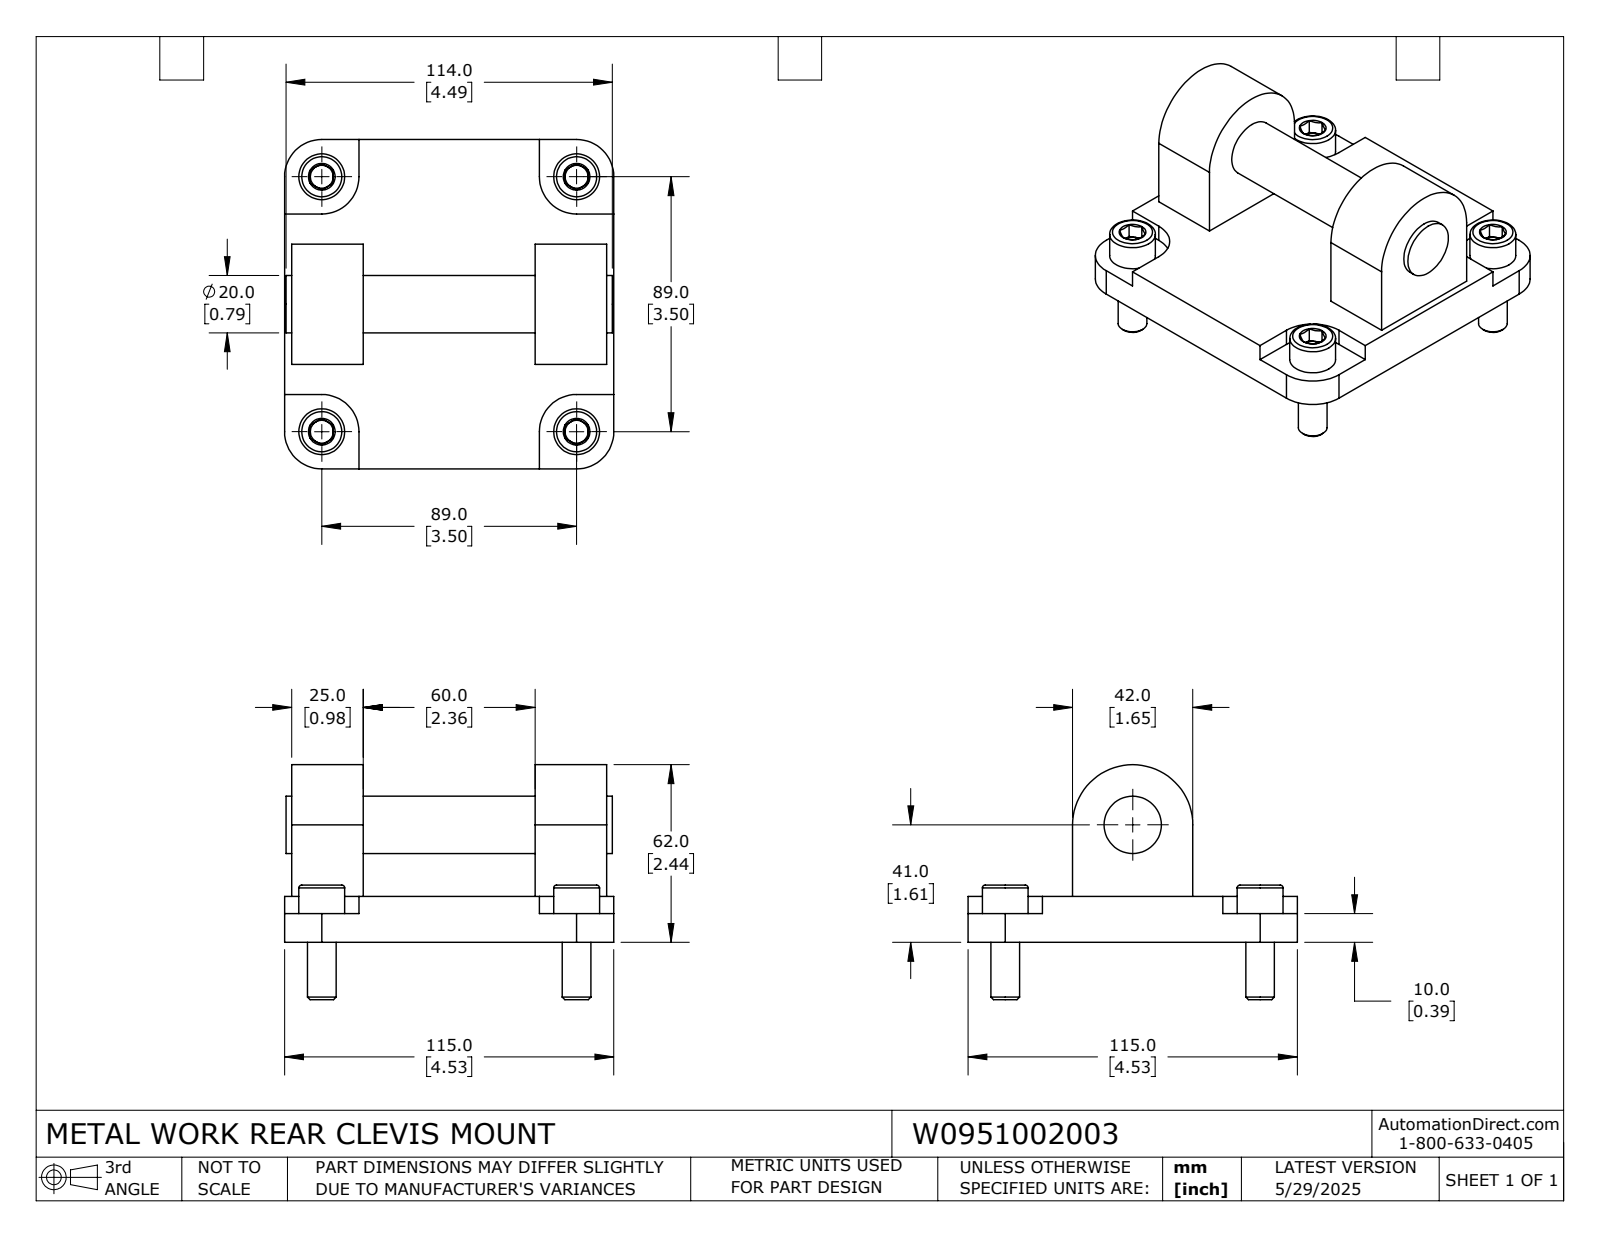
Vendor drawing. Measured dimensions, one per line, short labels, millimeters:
name: W0951002003
written by: SolidWorks 2024 (CONFIG_CONTROL_DESIGN)
unit: mm
bodies: 5 solids, 187 faces (89 planar, 42 cylindrical, 56 other)
size: 115 × 115 × 82
volume: 293 000 mm³; area: 57 150 mm²
holes: 4× ⌀11, 1× ⌀55
bosses: 4× ⌀16, 4× ⌀10, 1× ⌀20
rounds: 4× R13, 1× R21
face distances: 16, 85, 25, 10, 78.5, 36.5, 9, 2.5, 27.5, 87.5
hole spacings: 62.9, 89, 125.9
